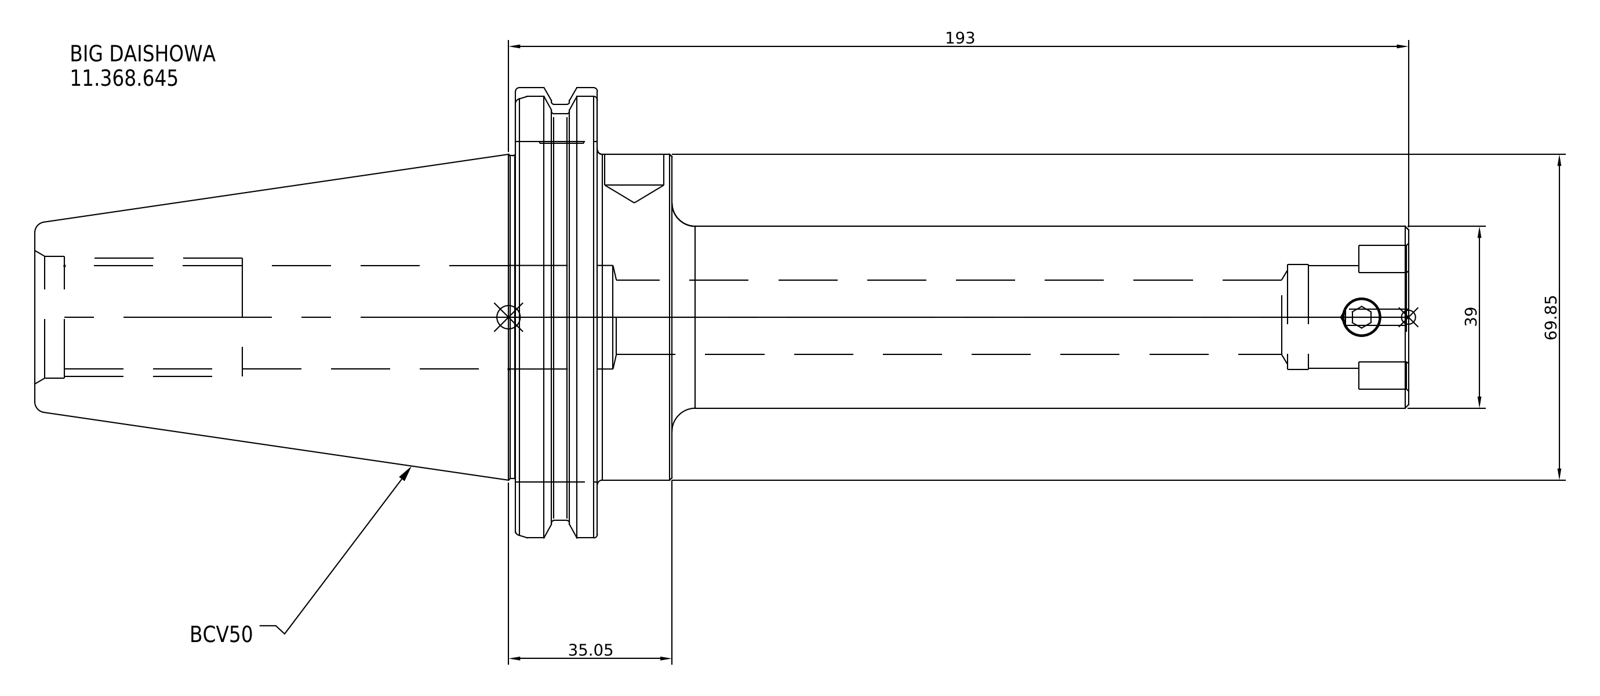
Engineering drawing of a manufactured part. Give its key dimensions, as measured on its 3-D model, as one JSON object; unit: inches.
{"part_name": "11.368.645", "step_written_by": "SolidWorks 2021 (CONFIG_CONTROL_DESIGN)", "units": "inches", "bodies": {"solids": 1, "faces": 16, "planar": 7, "cylindrical": 6, "other": 3}, "overall_size": [11.598, 3.875, 3.875], "volume_in3": 38.52, "surface_area_in2": 93.51, "round_bosses_or_shafts": [[3.875, 1], [3.594, 1], [2.75, 1], [1.535, 1]], "face_to_face_distances": [0.691, 0.628, 1.319, 5.378, 4.75, 4.059, 6.22, 6.848, 7.539, 11.598]}
